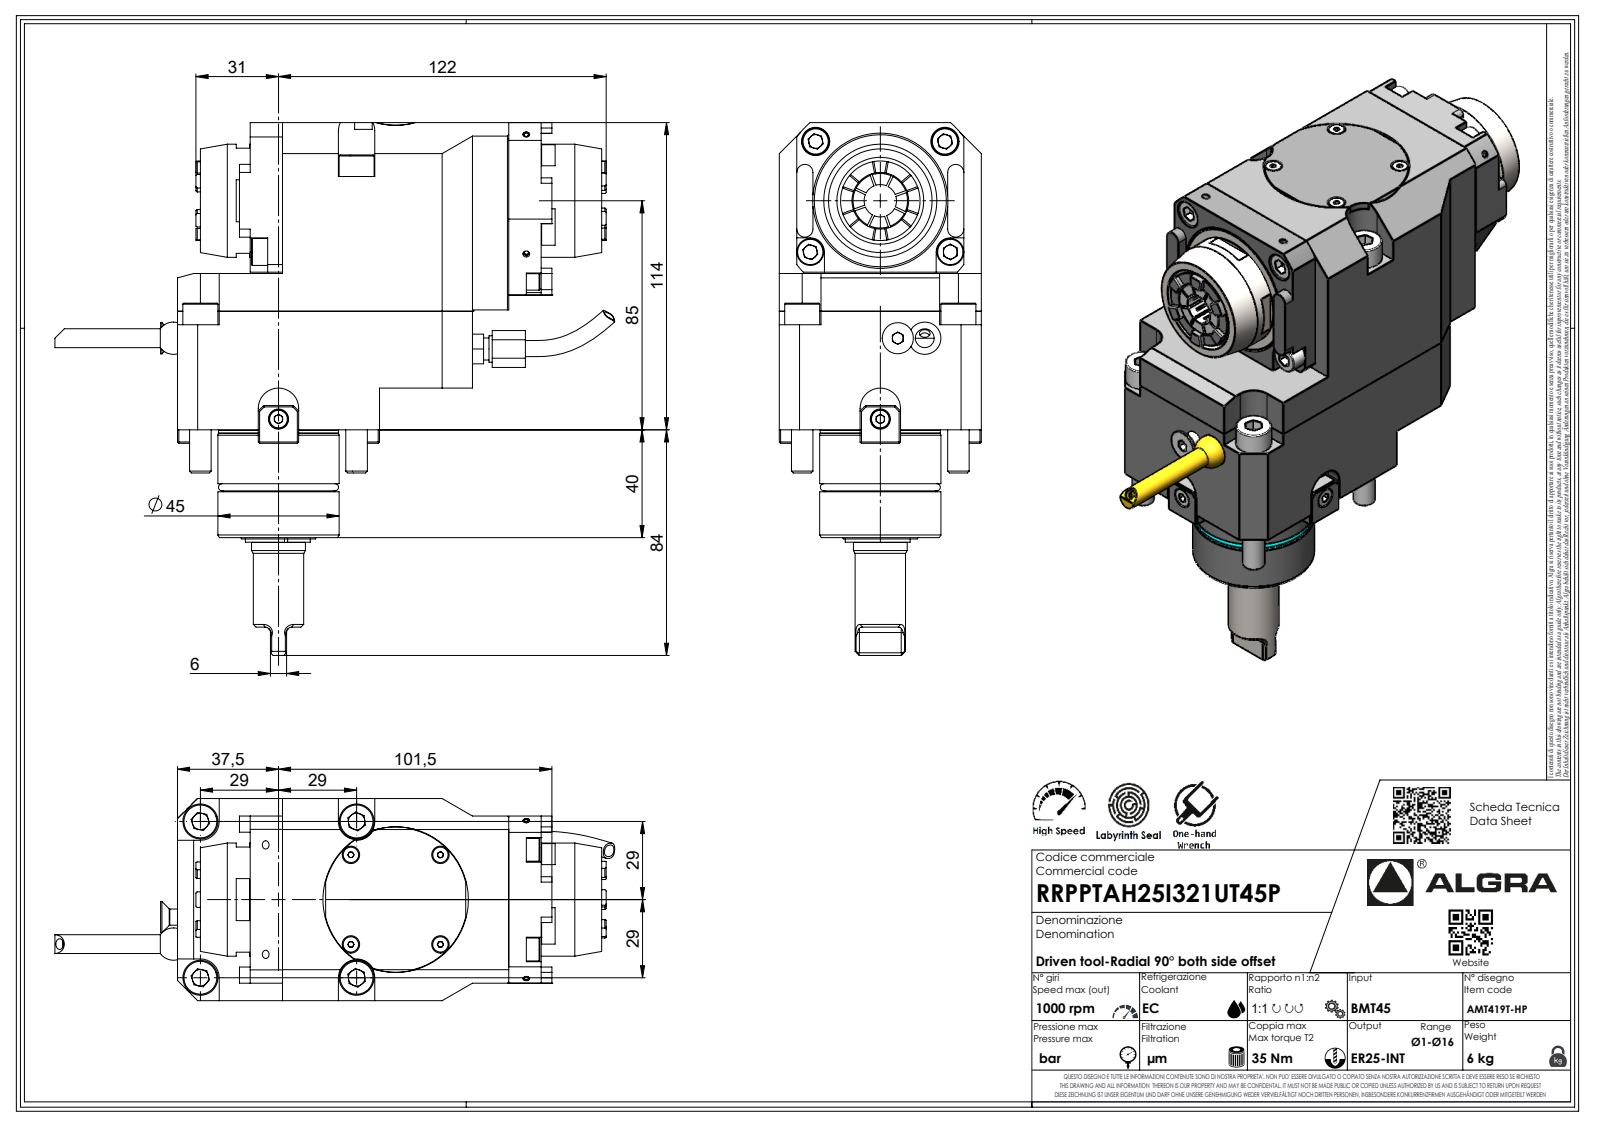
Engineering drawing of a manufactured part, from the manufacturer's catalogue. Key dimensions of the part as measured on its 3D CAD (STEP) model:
Part name (STEP PRODUCT): RRPPTAH25I321UT45P
STEP written by: SolidWorks 2023 (AUTOMOTIVE_DESIGN)
Units: millimetres
Bodies: 1 solid, 687 faces (480 planar, 91 cylindrical, 116 other)
Overall size (bounding box): 207.81 × 197.7 × 75
Volume: 984 540 mm³ · Surface area: 81 128 mm²
Round holes (diameter × count): ⌀2.1 ×1, ⌀4 ×1
Round bosses / shafts (diameter × count): ⌀13 ×4, ⌀8 ×4, ⌀45 ×1, ⌀44.6 ×1, ⌀42 ×1, ⌀41 ×1, ⌀20 ×1, ⌀19 ×1
Partial cylindrical surfaces — rounded edges, fillets, slot ends (radius × count): R2 ×19, R0.33 ×7, R0.52 ×7, R3.7 ×7, R3 ×4, R6.75 ×2, R7 ×2, R0.21 ×1
Main face-to-face distances: 75, 6.5, 68.5, 98.5, 114, 15.5, 48, 82.5, 34.5, 56
